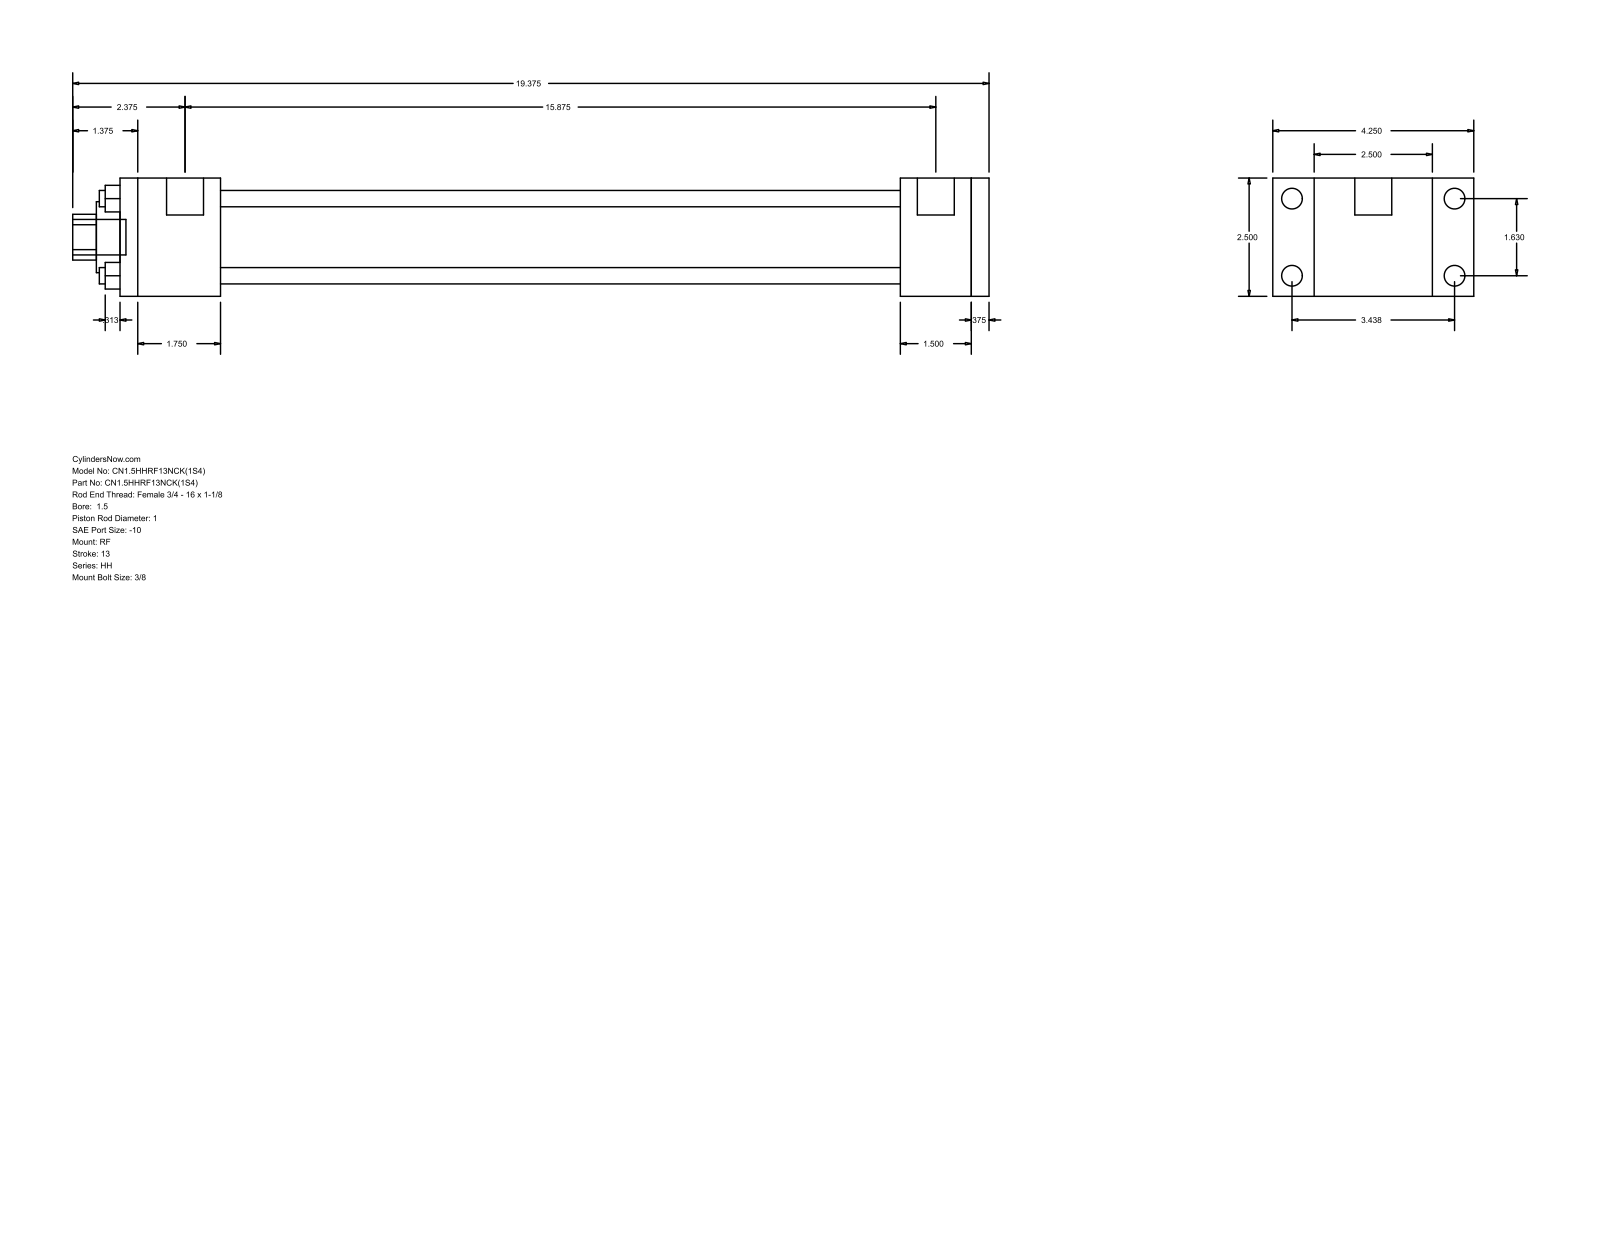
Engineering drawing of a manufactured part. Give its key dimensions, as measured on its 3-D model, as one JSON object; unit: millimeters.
{"part_name": "HH_RF__0150_1", "step_written_by": "GSSL Pune (CONFIG_CONTROL_DESIGN)", "units": "millimeters", "bodies": {"solids": 0, "faces": 92, "planar": 64, "cylindrical": 28, "other": 0}, "overall_size": [492.12, 107.95, 63.5], "round_holes": [[8.76, 4], [25.4, 1], [38.1, 1], [44.45, 1]], "round_bosses_or_shafts": [[11.13, 4], [5.56, 4], [19.84, 2], [19.05, 1]], "partial_cylinders_radius": [[12.29, 1]], "face_to_face_distances": [63.5, 9.52, 365.12, 403.22, 412.74, 38.1, 47.62, 53.98, 419.1, 457.2], "hole_center_spacings": [29.27, 41.4, 58.55]}
